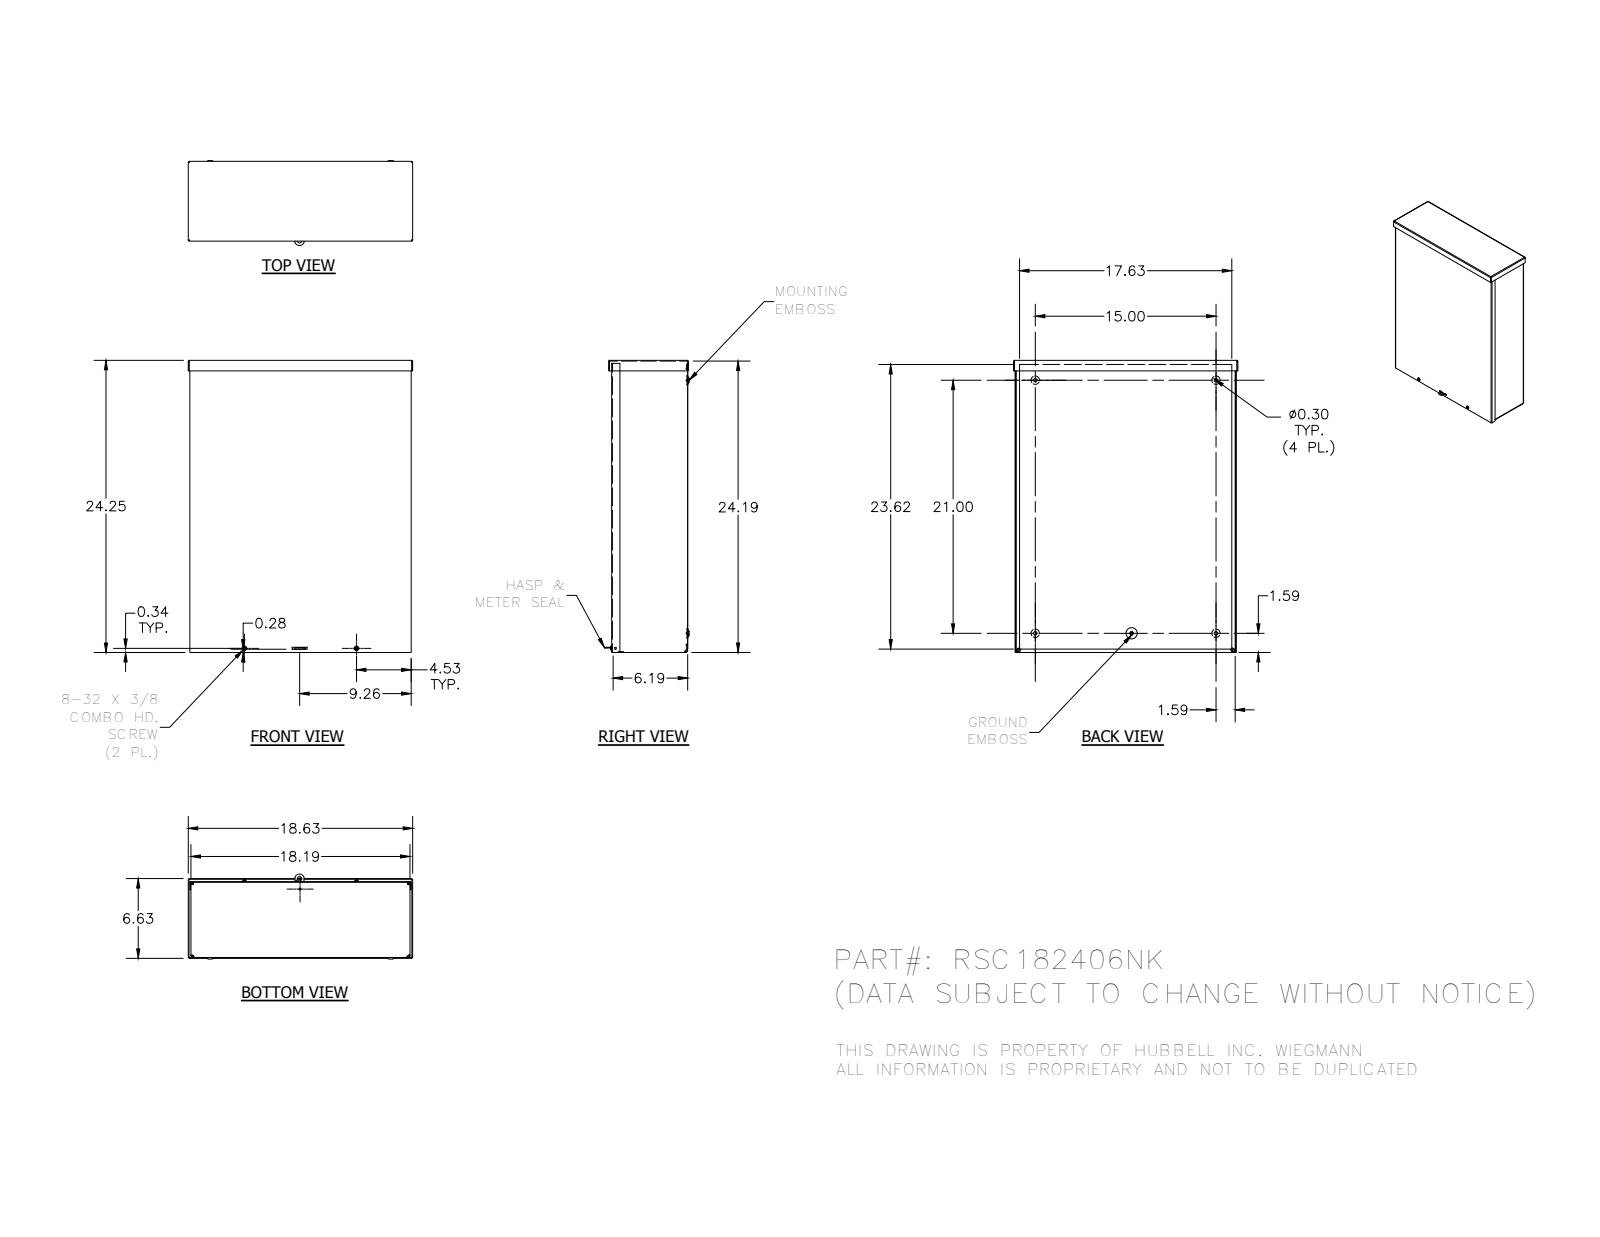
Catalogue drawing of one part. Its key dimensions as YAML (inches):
part_name: "RSC182406NK_WRAP; RSC1824NK_LID; RSC1806NK_CAP; 3183 (+3 more)"
step_written_by: "Autodesk Inventor 2014 (AUTOMOTIVE_DESIGN)"
units: inches
bodies: {solids: 7, faces: 377, planar: 163, cylindrical: 78, other: 136}
overall_size: [24.25, 18.625, 7.125]
volume: 105.1
surface_area: 3413
round_holes:
  - {diameter: 0.3, count: 4}
  - {diameter: 0.313, count: 4}
  - {diameter: 0.148, count: 2}
  - {diameter: 0.125, count: 1}
  - {diameter: 0.136, count: 1}
  - {diameter: 0.156, count: 1}
  - {diameter: 0.165, count: 1}
  - {diameter: 0.375, count: 1}
round_bosses_or_shafts:
  - {diameter: 0.384, count: 2}
  - {diameter: 0.164, count: 2}
  - {diameter: 0.228, count: 1}
partial_cylinders:
  - {radius: 0.031, count: 8}
  - {radius: 0.093, count: 8}
  - {radius: 0.125, count: 8}
  - {radius: 0.187, count: 8}
  - {radius: 0.055, count: 4}
  - {radius: 0.062, count: 4}
  - {radius: 0.094, count: 4}
  - {radius: 0.117, count: 4}
face_to_face_distances: [0.062, 6.249, 6.187, 0.063, 6.312, 6.25, 0.062, 18.126, 24.126, 0.124]
hole_center_spacings: [9.313, 15, 21, 22.432, 23.312, 25.104, 25.189, 25.807]
